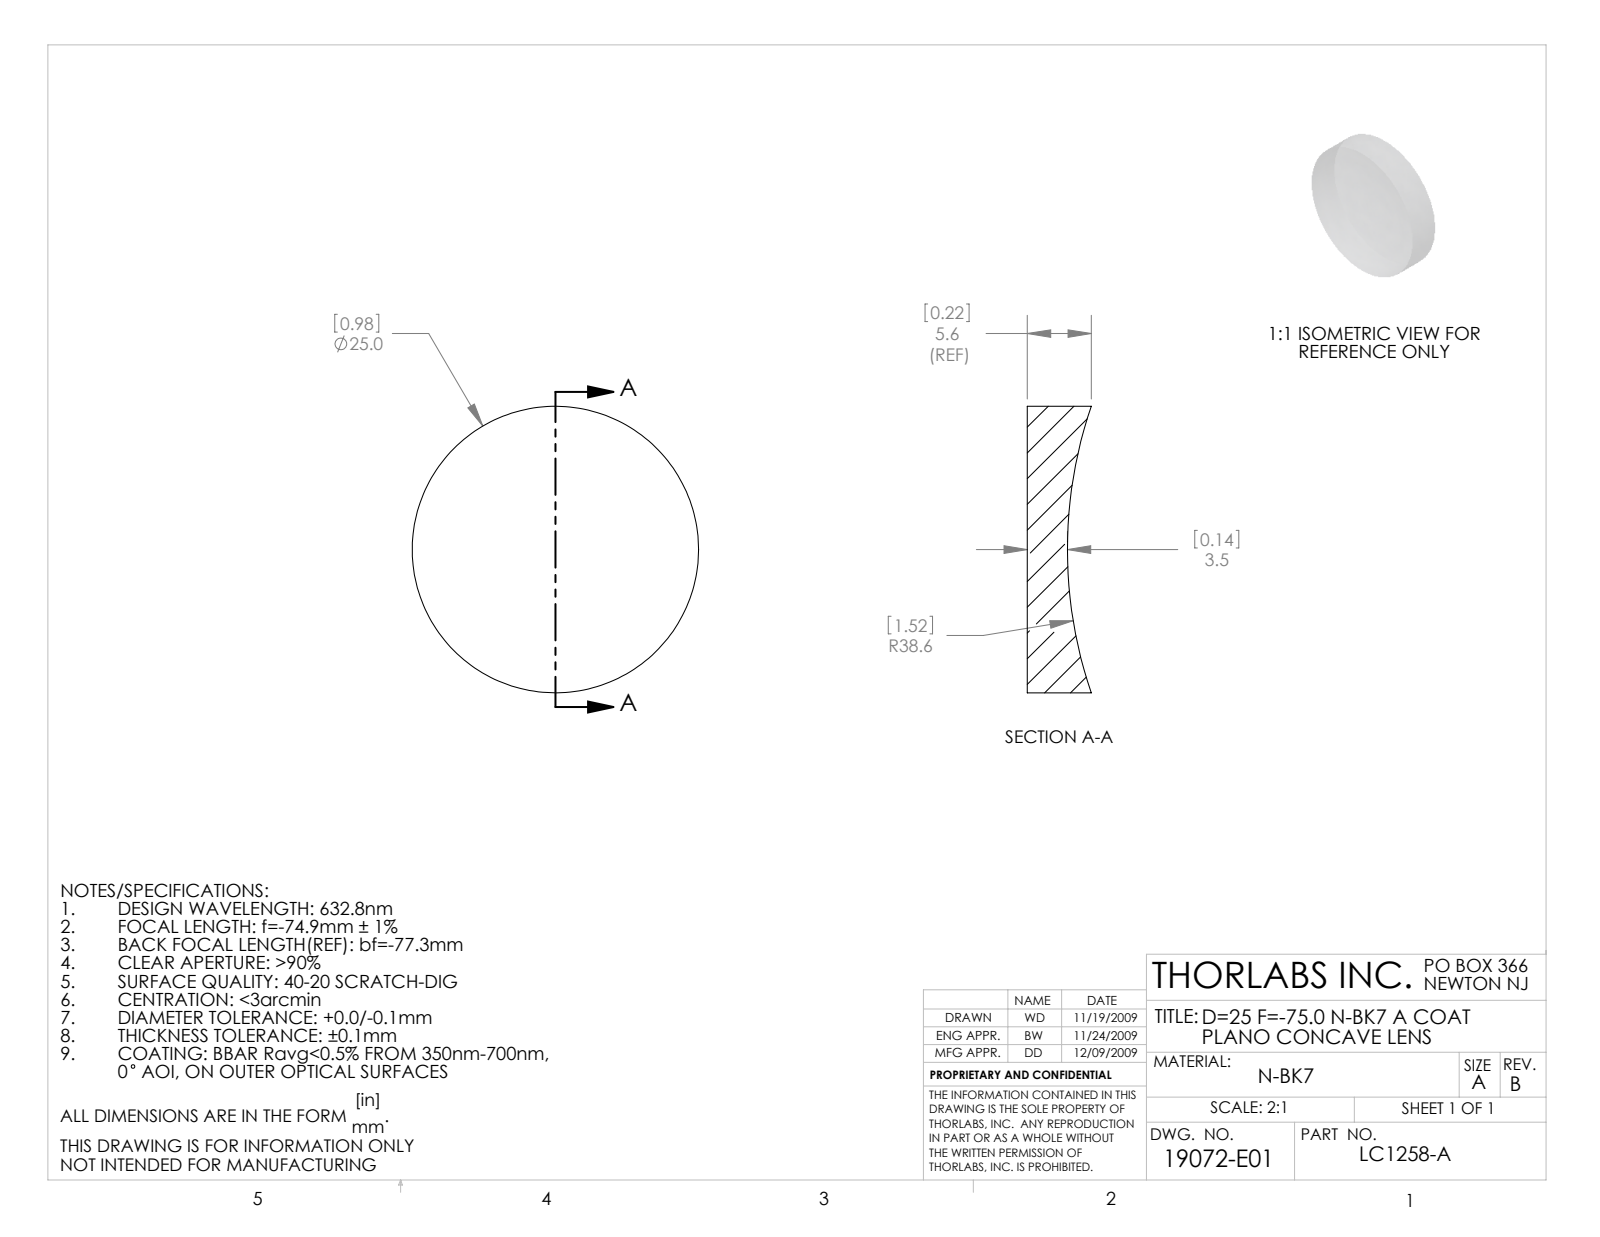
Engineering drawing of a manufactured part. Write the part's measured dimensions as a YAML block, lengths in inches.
part_name: "19072-E0W"
step_written_by: "SolidWorks 2009 (AUTOMOTIVE_DESIGN)"
units: inches
bodies: {solids: 1, faces: 5, planar: 1, cylindrical: 2, other: 2}
overall_size: [0.984, 0.984, 0.22]
volume: 0.136
surface_area: 2.223
round_bosses_or_shafts:
  - {diameter: 0.984, count: 1}
